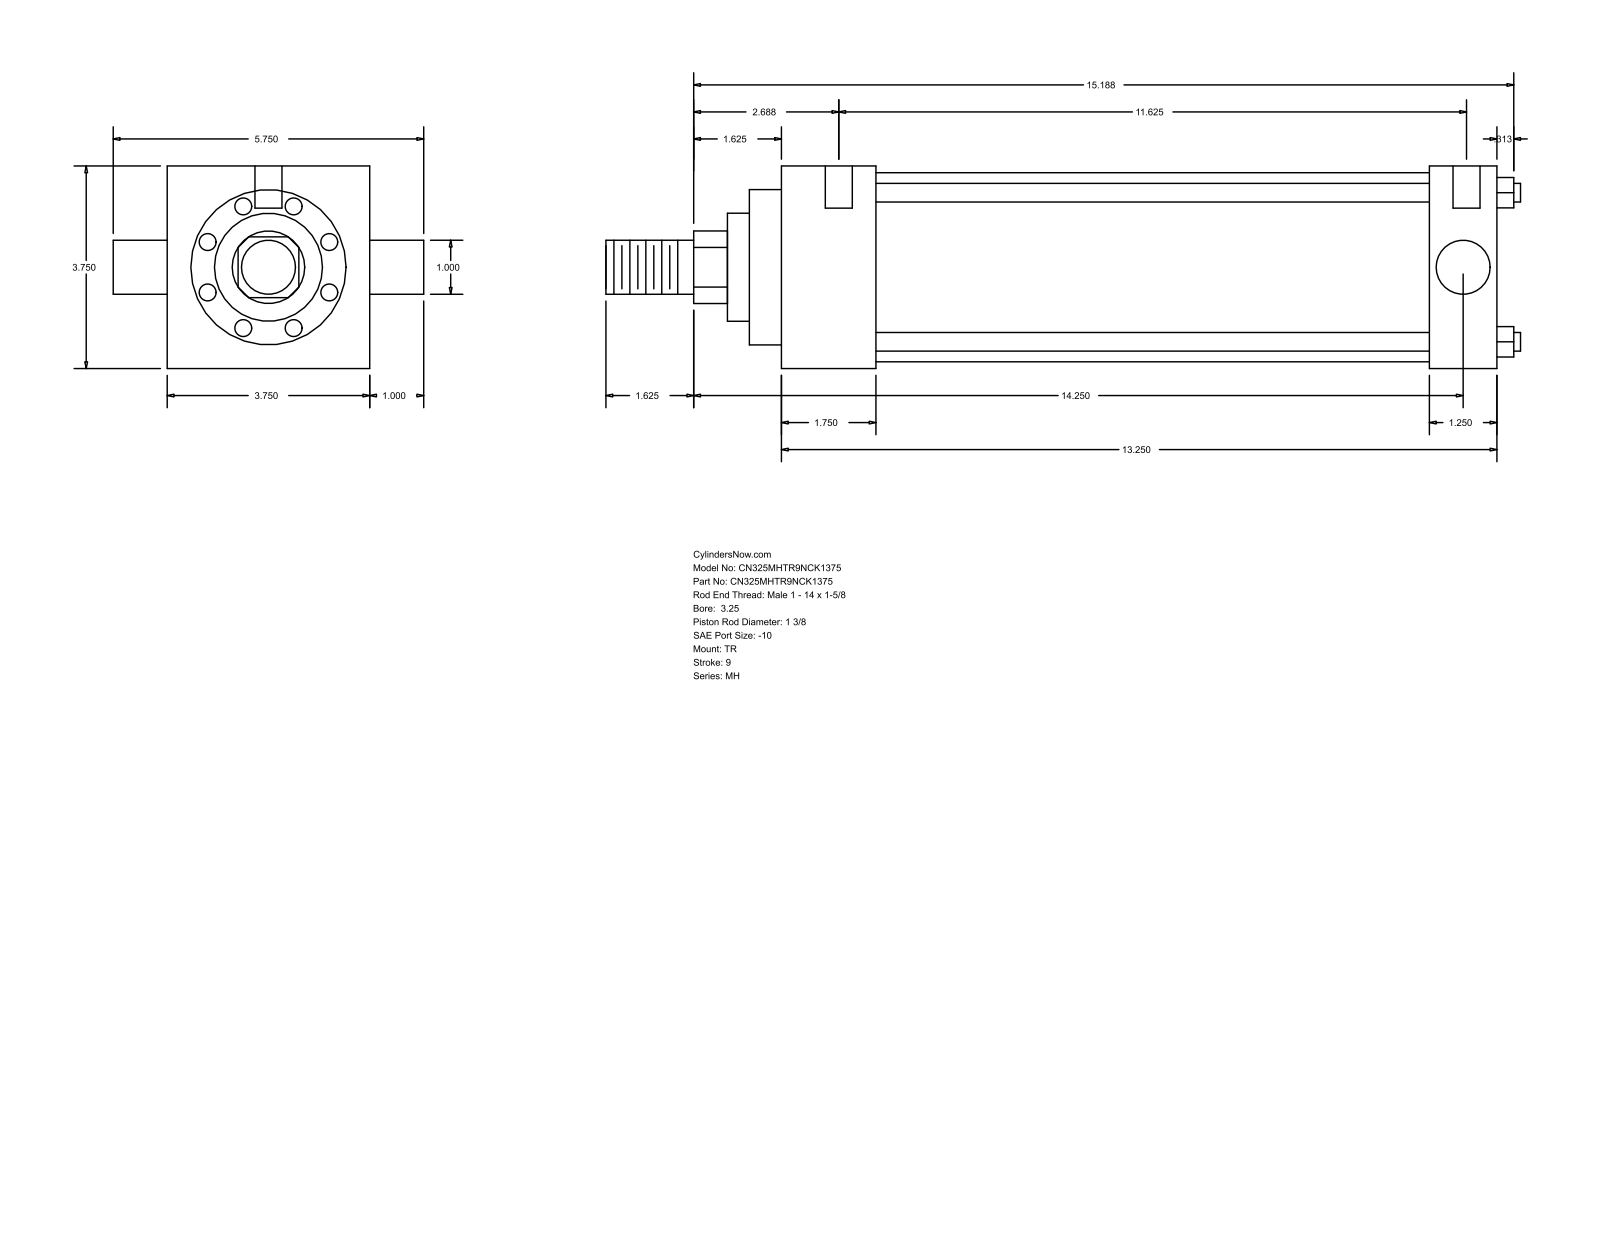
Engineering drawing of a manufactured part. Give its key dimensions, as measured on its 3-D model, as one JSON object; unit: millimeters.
{"part_name": "MH_TR__0325_1.375", "step_written_by": "GSSL Pune (CONFIG_CONTROL_DESIGN)", "units": "millimeters", "bodies": {"solids": 0, "faces": 86, "planar": 61, "cylindrical": 25, "other": 0}, "overall_size": [430.21, 146.05, 95.25], "round_holes": [[5.56, 3], [12.7, 2]], "round_bosses_or_shafts": [[8.76, 4], [25.4, 2], [88.9, 1], [73.03, 1], [50.8, 1], [34.92, 1]], "partial_cylinders_radius": [[17.06, 1]], "face_to_face_distances": [95.24, 336.55, 44.45, 304.8, 260.35, 292.1, 31.75, 15.08, 59.53, 319.88], "hole_center_spacings": [1.59, 4.76, 295.28, 296.87, 300.04, 301.63]}
